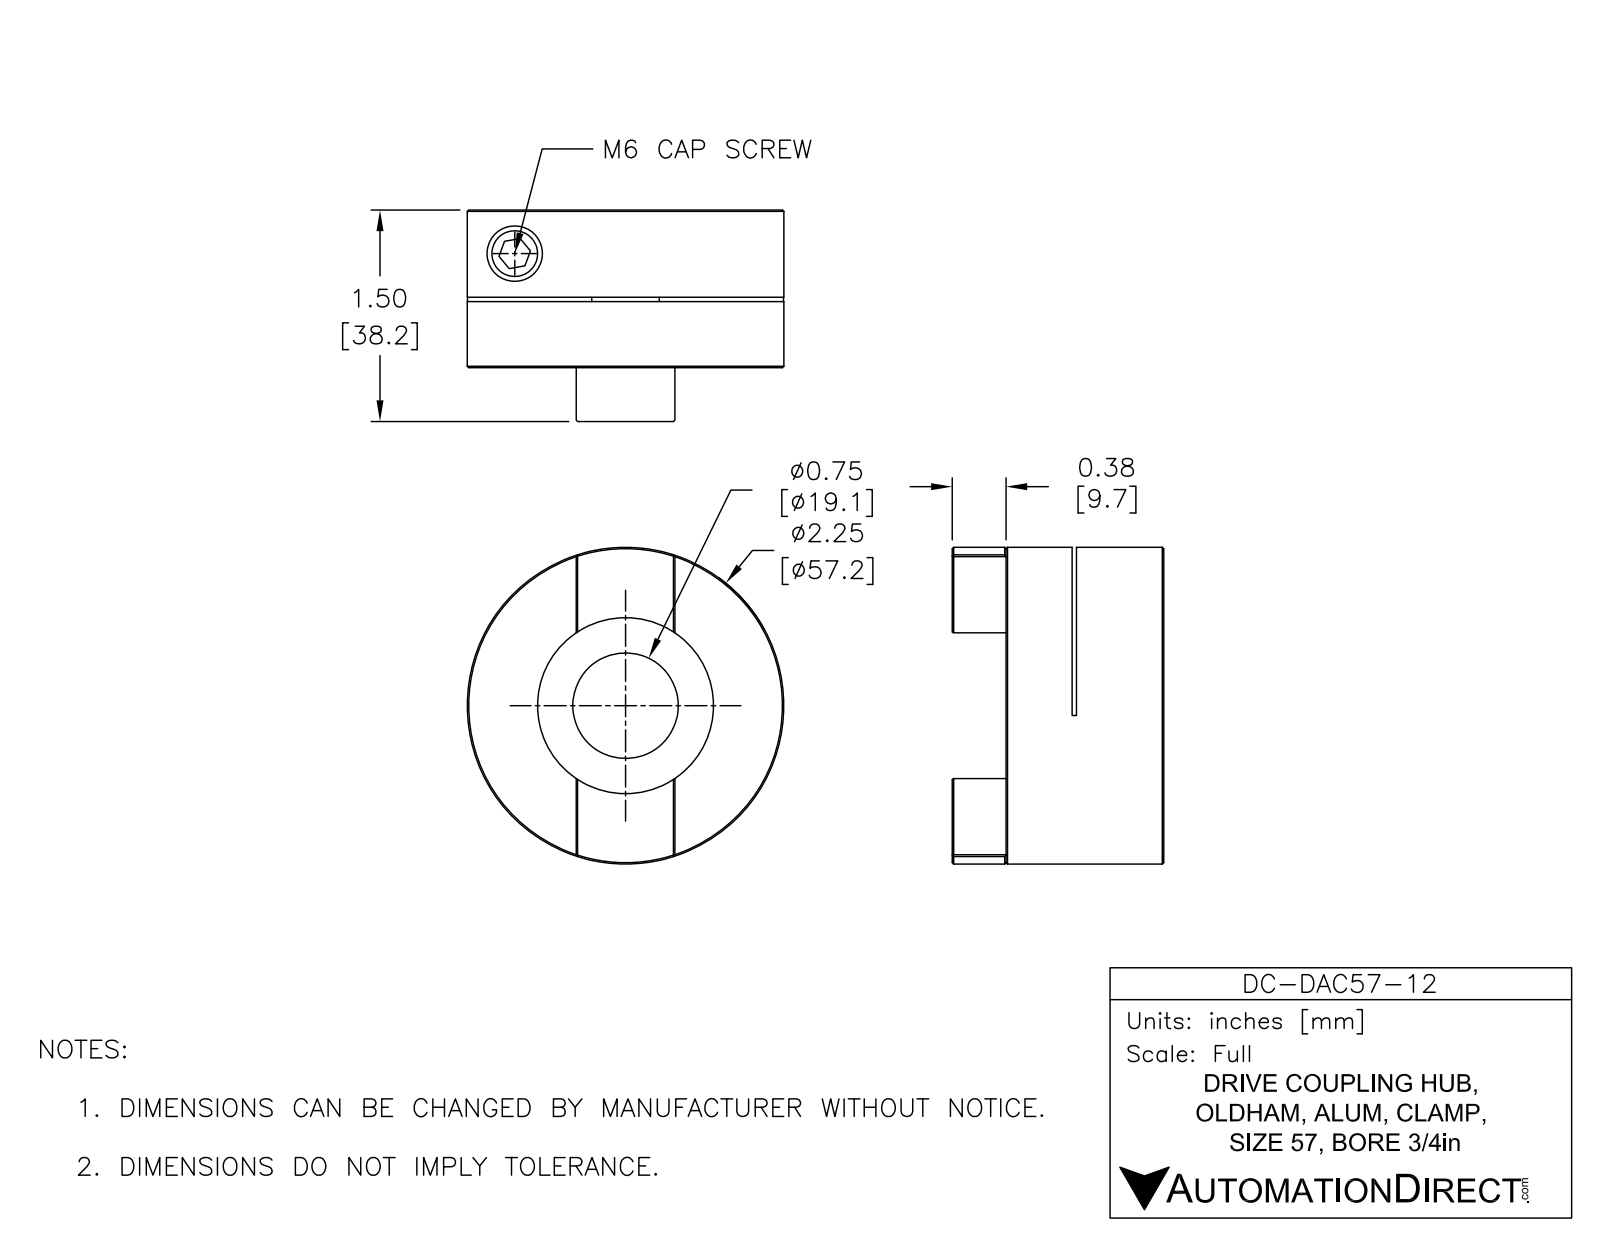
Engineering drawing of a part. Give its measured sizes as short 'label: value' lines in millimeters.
name: DC-DAC57-12
written by: SolidWorks 2015 (AUTOMOTIVE_DESIGN)
unit: mm
bodies: 1 solid, 53 faces (29 planar, 16 cylindrical, 8 other)
size: 57.15 × 57.15 × 38.16
volume: 69 905 mm³; area: 16 395 mm²
holes: 1× ⌀6.6, 1× ⌀11, 1× ⌀12.7, 1× ⌀31.75
bosses: 1× ⌀57.15
face distances: 16.54, 28.45, 11.91, 15.75, 0.79, 12.7, 28, 12.25, 11.46, 0.45
